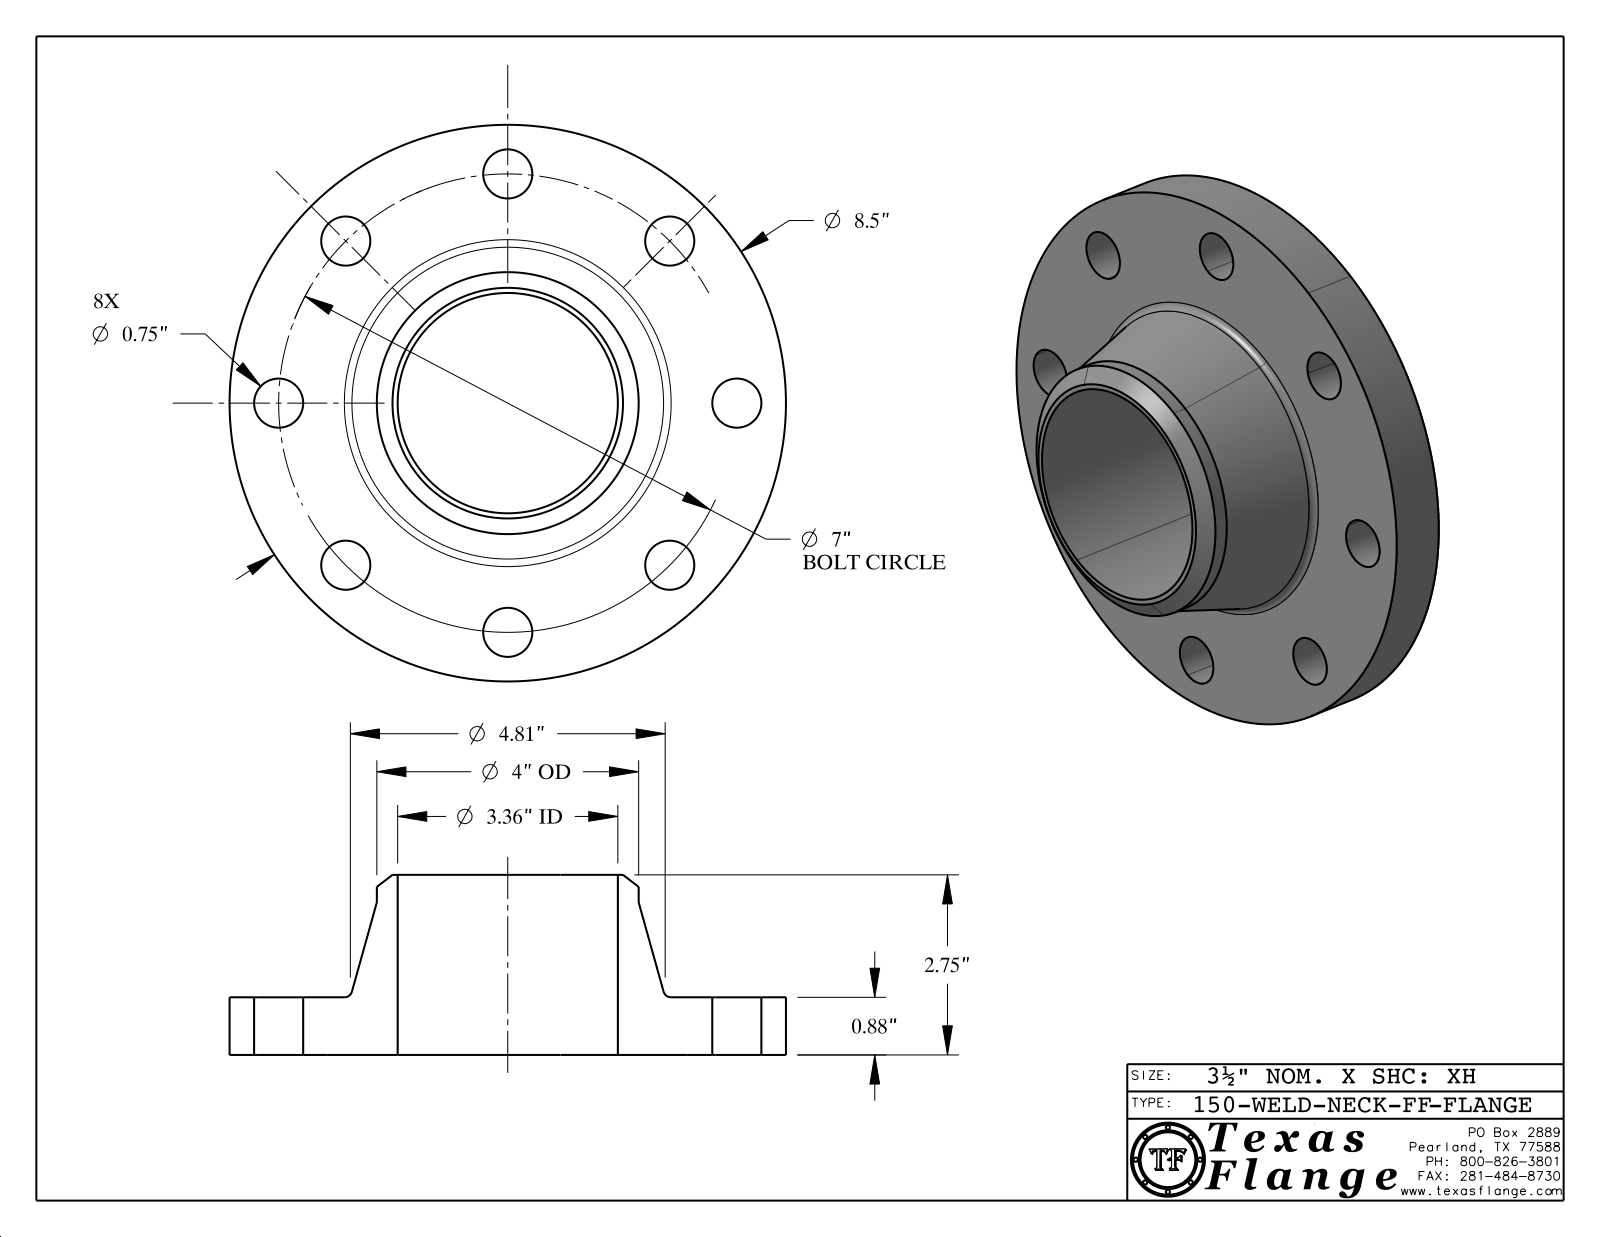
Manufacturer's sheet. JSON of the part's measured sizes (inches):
{"part_name": "150-WELD-NECK-FF", "step_written_by": "CATIA V5 STEP AP214 (AUTOMOTIVE_DESIGN)", "units": "inches", "bodies": {"solids": 1, "faces": 417, "planar": 369, "cylindrical": 42, "other": 6}, "overall_size": [8.5, 8.5, 2.75], "volume_in3": 49.58, "surface_area_in2": 176.4, "round_holes": [[0.75, 8], [0.495, 1], [3.364, 1]], "round_bosses_or_shafts": [[0.03, 8], [8.5, 1], [4, 1], [0.39, 1]], "face_to_face_distances": [0.88, 2.75, 1.87, 0.865, 0.015, 1.885, 0.148, 0.145, 0.027, 0.096], "hole_center_spacings": [3.5, 2.679, 4.95, 6.467, 1.366, 3.889, 5.82, 6.865]}
